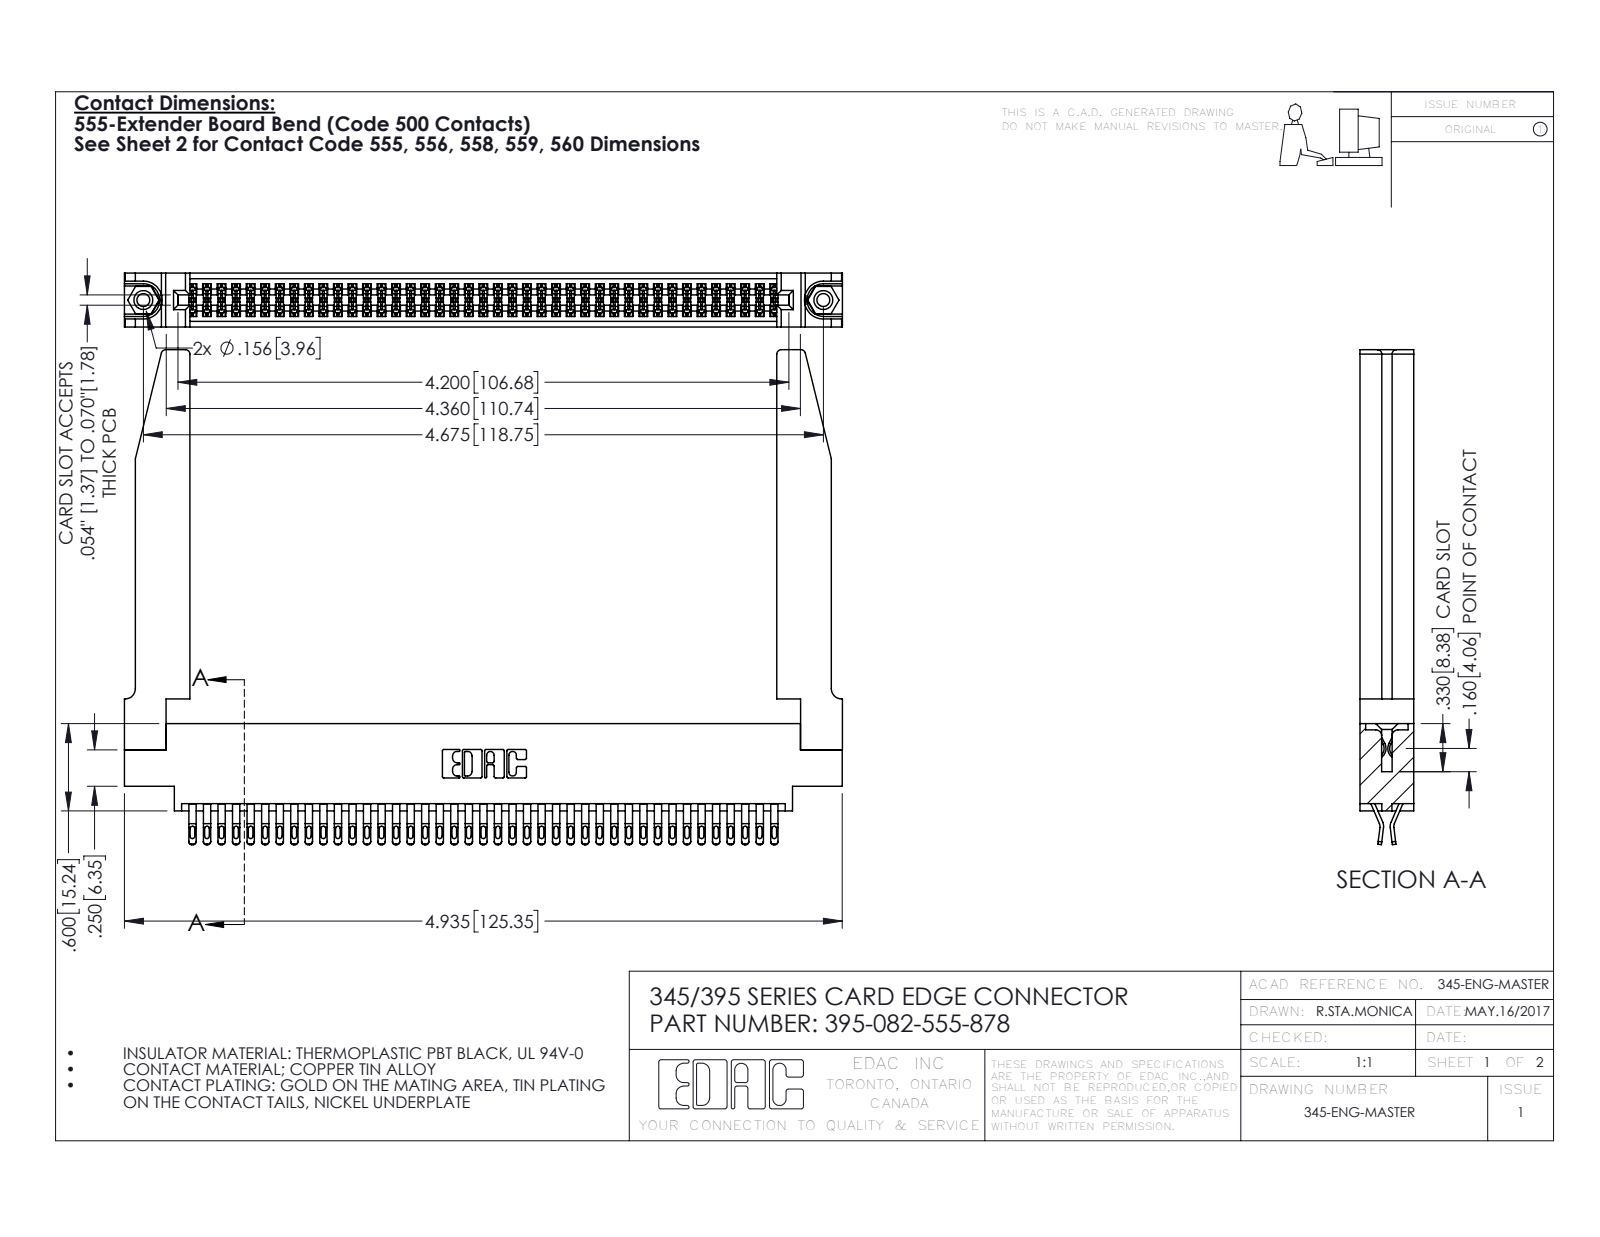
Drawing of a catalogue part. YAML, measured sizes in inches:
part_name: "345-250-001_345-250-001-102; 345 Part_0.170 Offset - 0.156 Dia-TH; 345-220-078_345-220-078; 395-082-555-878 (+1 more)"
step_written_by: "SolidWorks 2016 (CONFIG_CONTROL_DESIGN)"
units: inches
bodies: {solids: 87, faces: 4956, planar: 2768, cylindrical: 2136, other: 52}
overall_size: [4.936, 3.402, 0.37]
volume: 1.224
surface_area: 40.24
round_holes:
  - {diameter: 0.089, count: 2}
  - {diameter: 0.125, count: 2}
  - {diameter: 0.156, count: 2}
  - {diameter: 0.064, count: 1}
round_bosses_or_shafts:
  - {diameter: 0.155, count: 2}
partial_cylinders:
  - {radius: 0.016, count: 205}
  - {radius: 0.02, count: 164}
  - {radius: 0.006, count: 123}
  - {radius: 0.01, count: 22}
  - {radius: 0.03, count: 8}
  - {radius: 0.007, count: 6}
  - {radius: 0.031, count: 6}
  - {radius: 0.026, count: 3}
face_to_face_distances: [0.37, 0.072, 0.298, 0.025, 0.2, 0.098, 0.272, 0.225, 0.175, 0.148]
hole_center_spacings: [0.27, 4.439, 4.675]
